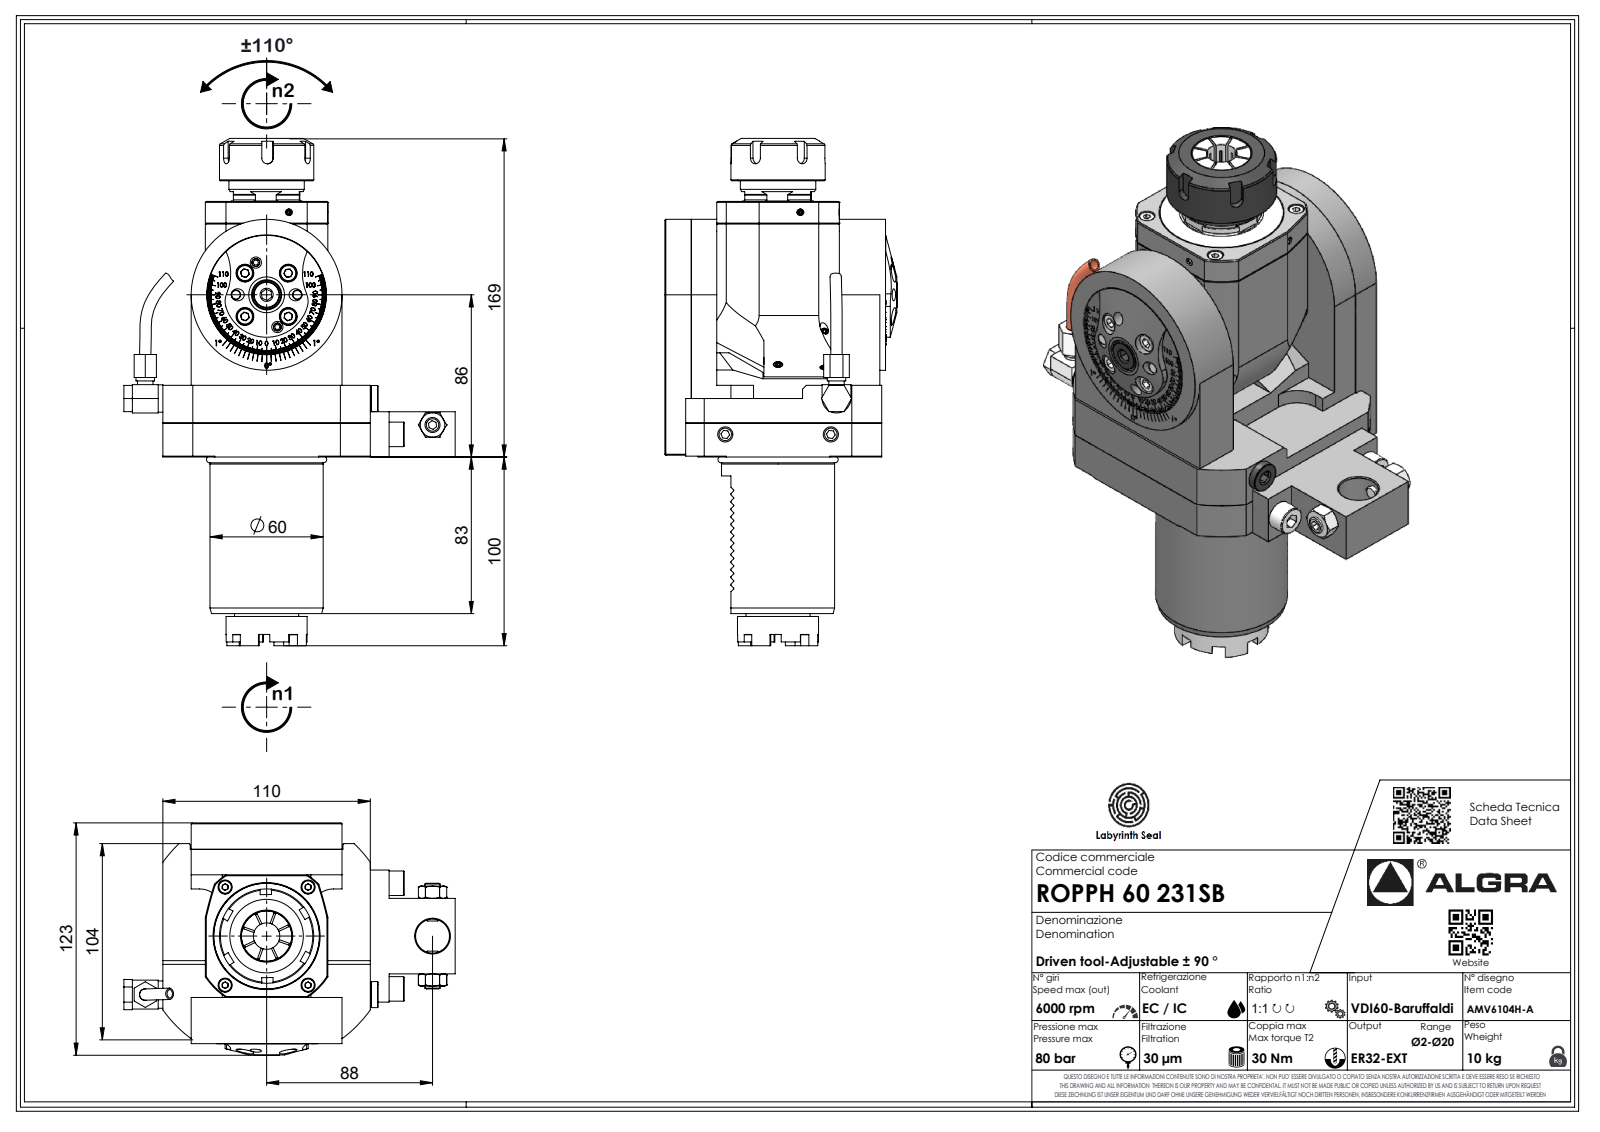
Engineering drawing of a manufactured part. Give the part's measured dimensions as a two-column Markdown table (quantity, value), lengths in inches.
| quantity | value |
| --- | --- |
| part name | ROPPH60231SD32 |
| STEP written by | SolidWorks 2023 (AUTOMOTIVE_DESIGN) |
| units | inches |
| bodies | 1 solid, 680 faces (420 planar, 105 cylindrical, 155 other) |
| overall size | 10.981 × 6.917 × 4.843 |
| volume | 89.34 in³ |
| surface area | 192 in² |
| round holes (diameter × count) | 0.083 × 1 |
| round bosses / shafts (diameter × count) | 3.15 × 1, 2.362 × 1, 2.311 × 1, 1.969 × 1, 1.575 × 1, 1.181 × 1, 1.142 × 1, 0.571 × 1 |
| partial cylindrical surfaces (radius × count) | 0.012 × 14, 0.118 × 11, 0.013 × 7, 0.02 × 7, 0.146 × 7, 0.008 × 3, 0.394 × 2, 0.472 × 2 |
| main face-to-face distances | 0.886, 3.445, 2.559, 3.15, 0.295, 0.276, 1.083, 0.591, 2.854, 3.74 |
